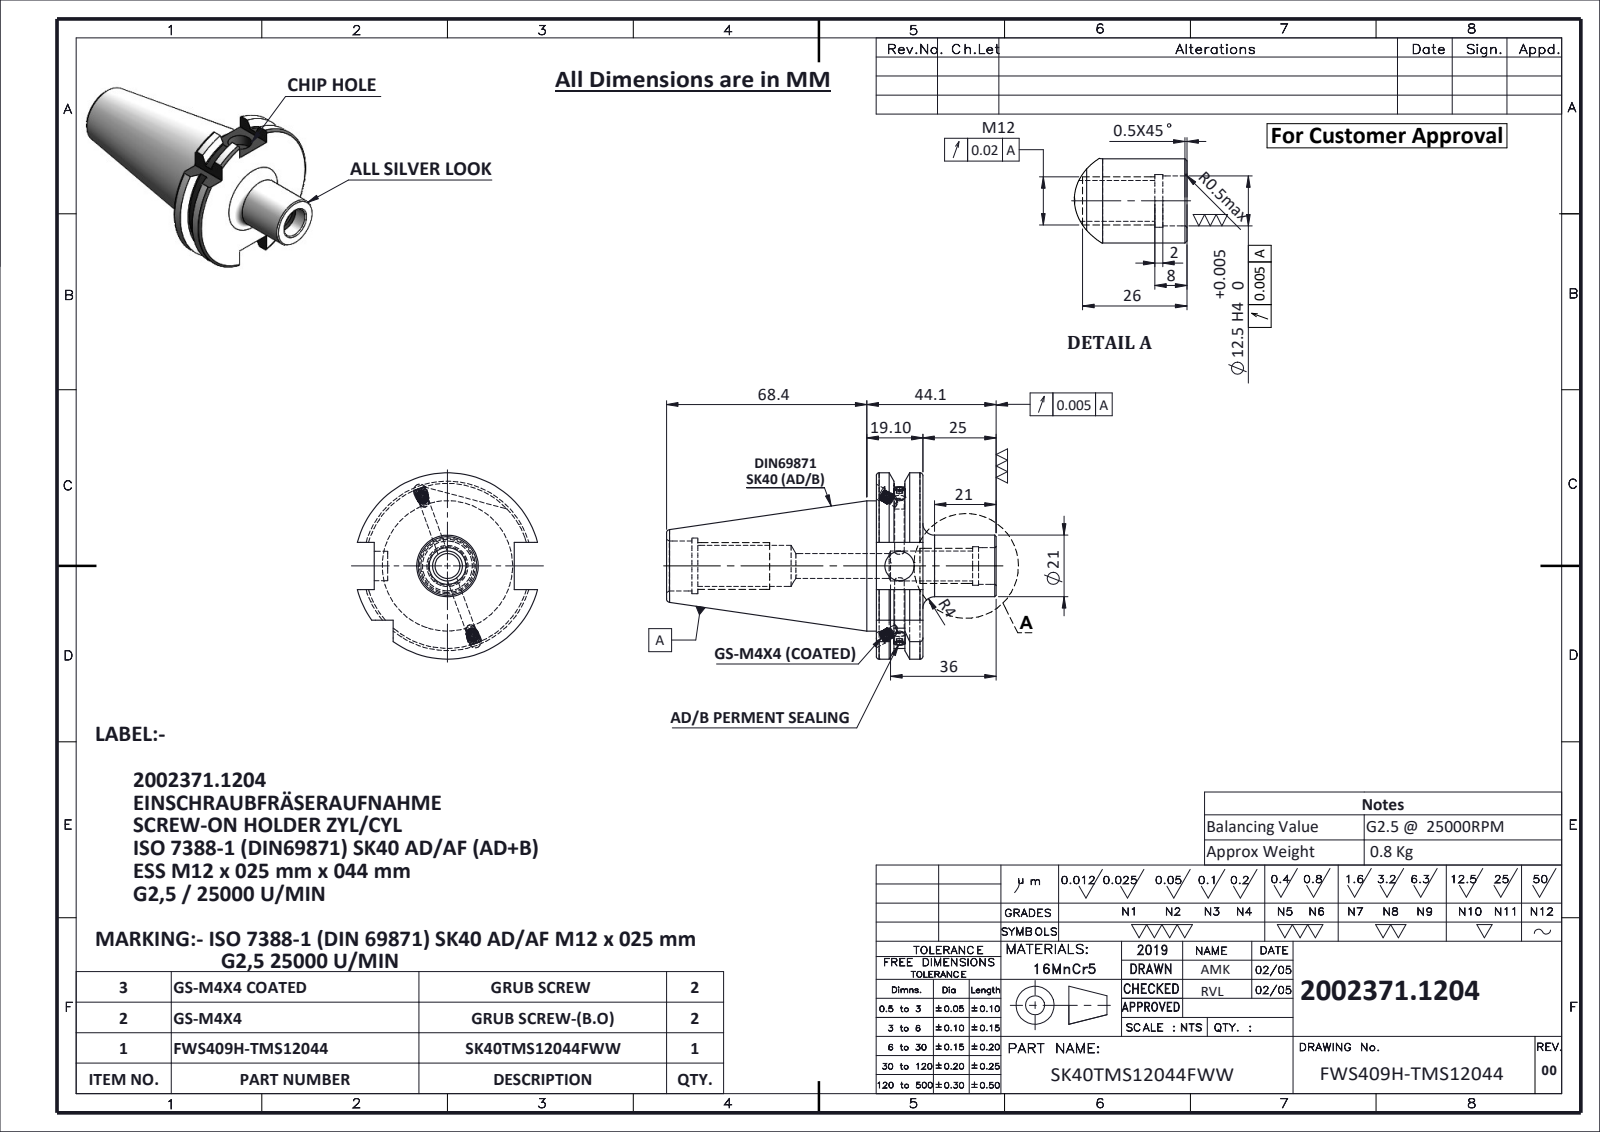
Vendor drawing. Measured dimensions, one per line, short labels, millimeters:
name: GS-M4X4-COATING_DIN 913 - M4 x 4-N; SK40TMS12044FWW; GS-M4X4_DIN 913 - M4 x 4-N; FWS409H-TMS12044
written by: SolidWorks 2024 (CONFIG_CONTROL_DESIGN)
unit: mm
bodies: 5 solids, 242 faces (64 planar, 72 cylindrical, 106 other)
size: 112.5 × 63.55 × 61.48
volume: 108 939 mm³; area: 23 479 mm²
holes: 3× ⌀3.3, 2× ⌀4.5, 1× ⌀8.5, 1× ⌀10, 1× ⌀10.2, 1× ⌀12.5, 1× ⌀13.1, 1× ⌀14, 1× ⌀17, 1× ⌀19
bosses: 4× ⌀4, 2× ⌀2.9, 1× ⌀44.45, 1× ⌀21
rounds: 1× R28.12, 1× R31.77
face distances: 15.9, 16.1, 47.8, 40.9, 25, 71.6, 87.5, 112.5, 10.7, 60.9
